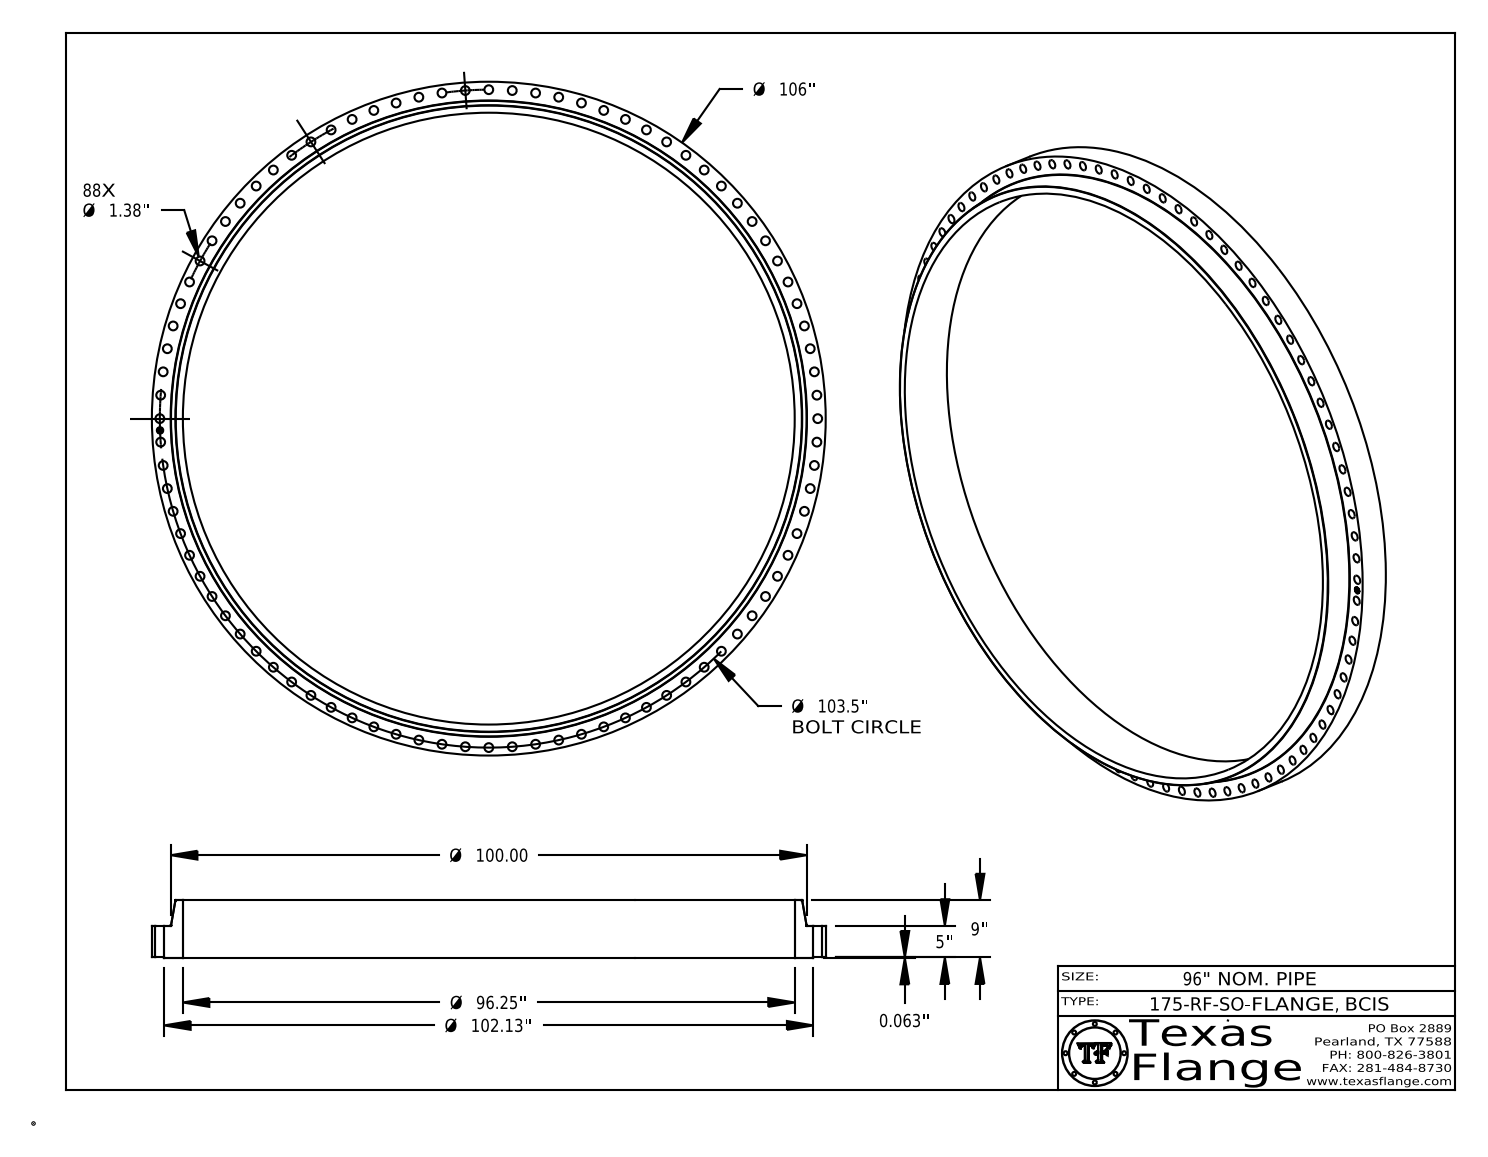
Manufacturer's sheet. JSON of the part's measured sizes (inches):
{"part_name": "175-RF-SO", "step_written_by": "CATIA V5 STEP AP214 (AUTOMOTIVE_DESIGN)", "units": "inches", "bodies": {"solids": 1, "faces": 663, "planar": 369, "cylindrical": 288, "other": 6}, "overall_size": [106, 106, 9.063], "volume_in3": 9014, "surface_area_in2": 10204, "round_holes": [[1.38, 88], [1, 1], [96.25, 1]], "round_bosses_or_shafts": [[0.061, 8], [106, 1], [102.13, 1], [0.788, 1]], "face_to_face_distances": [5.063, 0.063, 5, 9.063, 9, 4, 0.015, 5.048, 4.985, 4.015], "hole_center_spacings": [51.75, 3.694, 18.377, 22, 11.064, 32.685, 96.974, 7.383]}
